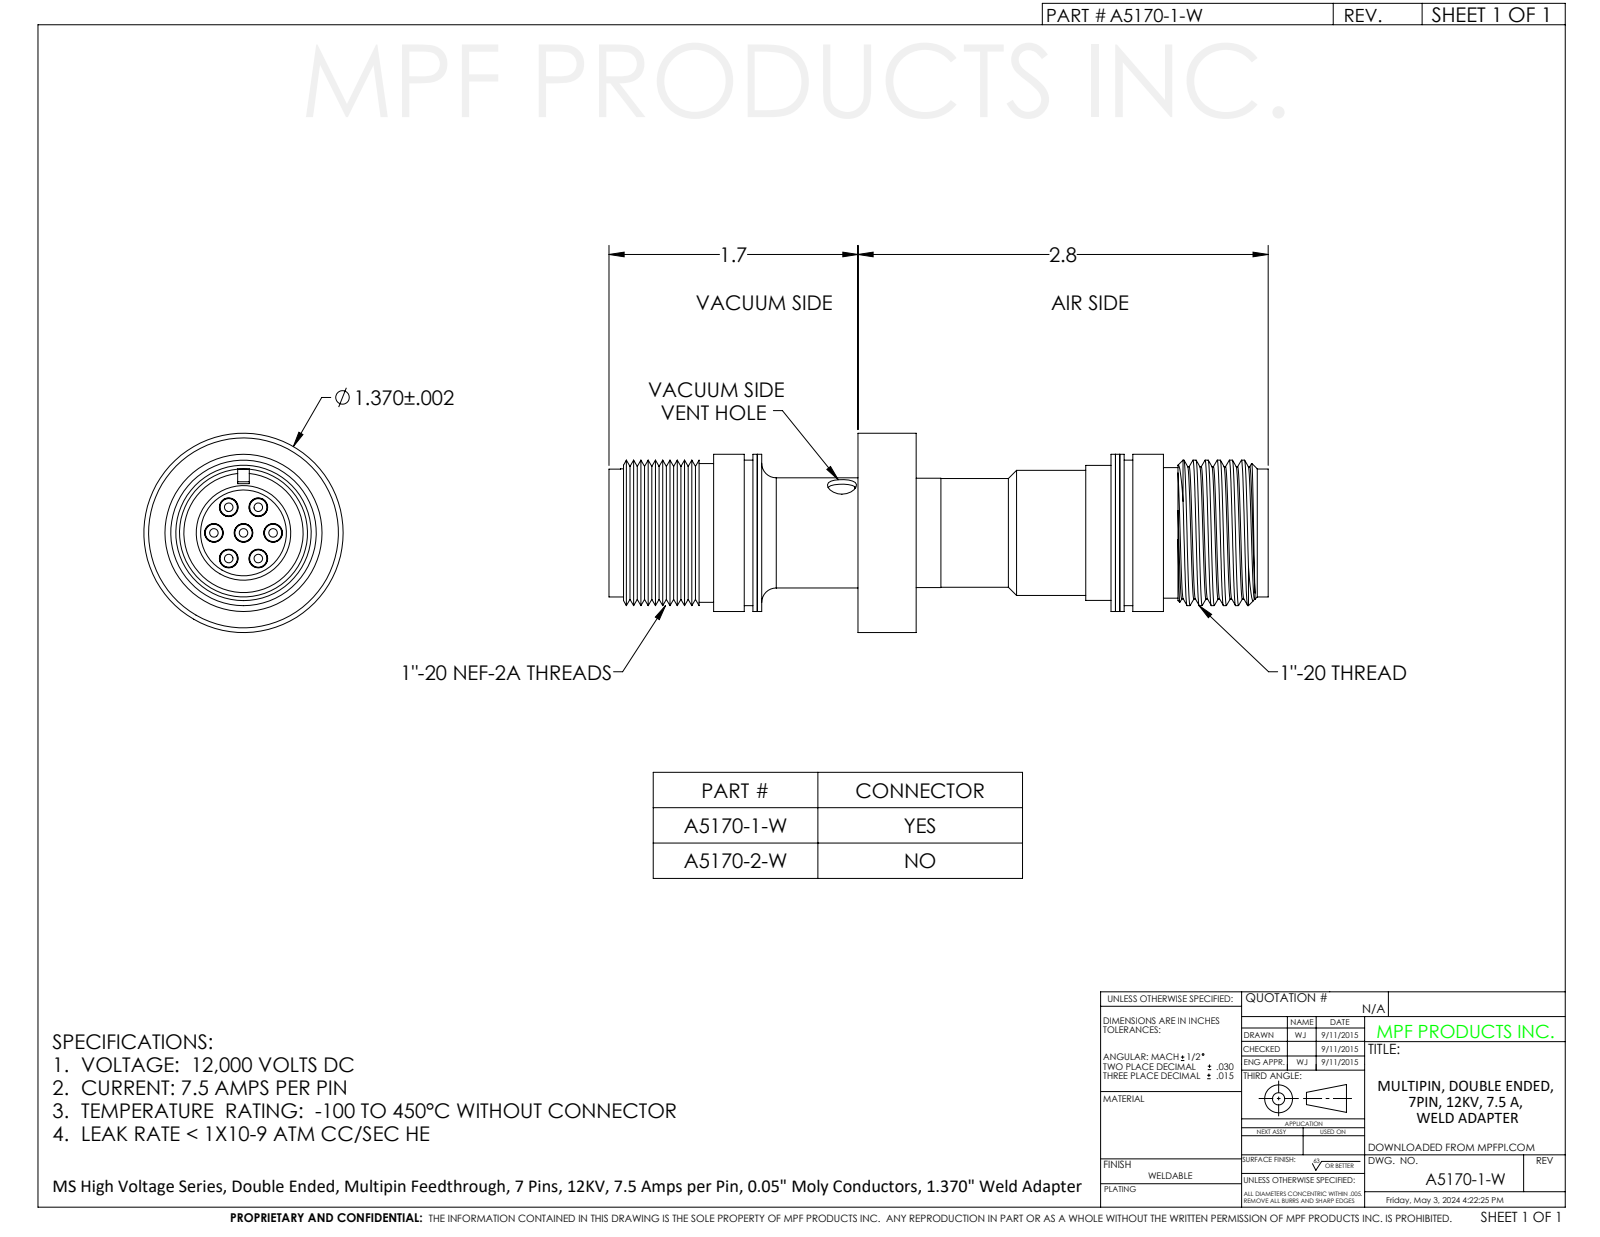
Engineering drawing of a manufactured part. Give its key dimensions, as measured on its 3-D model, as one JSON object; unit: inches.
{"part_name": "A5170-1-W", "step_written_by": "SolidWorks 2017 (CONFIG_CONTROL_DESIGN)", "units": "inches", "bodies": {"solids": 22, "faces": 731, "planar": 198, "cylindrical": 271, "other": 262}, "overall_size": [4.532, 1.37, 1.37], "volume_in3": 2.506, "surface_area_in2": 51.16, "round_holes": [[0.042, 7], [0.05, 7], [0.053, 7], [0.059, 7], [0.075, 7], [0.129, 7], [0.152, 7], [0.035, 3], [0.035, 3], [0.054, 1], [0.2, 1], [0.647, 1]], "round_bosses_or_shafts": [[0.14, 7], [0.13, 7], [0.125, 7], [0.072, 7], [0.051, 7], [0.04, 7], [1.37, 1], [1.08, 1]], "partial_cylinders_radius": [[0.425, 1]], "face_to_face_distances": [0.36, 0.4, 0.04, 1.7, 0.33, 2.762, 0.716, 1.076, 1.116, 0.62], "hole_center_spacings": [0.204, 0.352, 0.407, 0.203, 0.353]}
